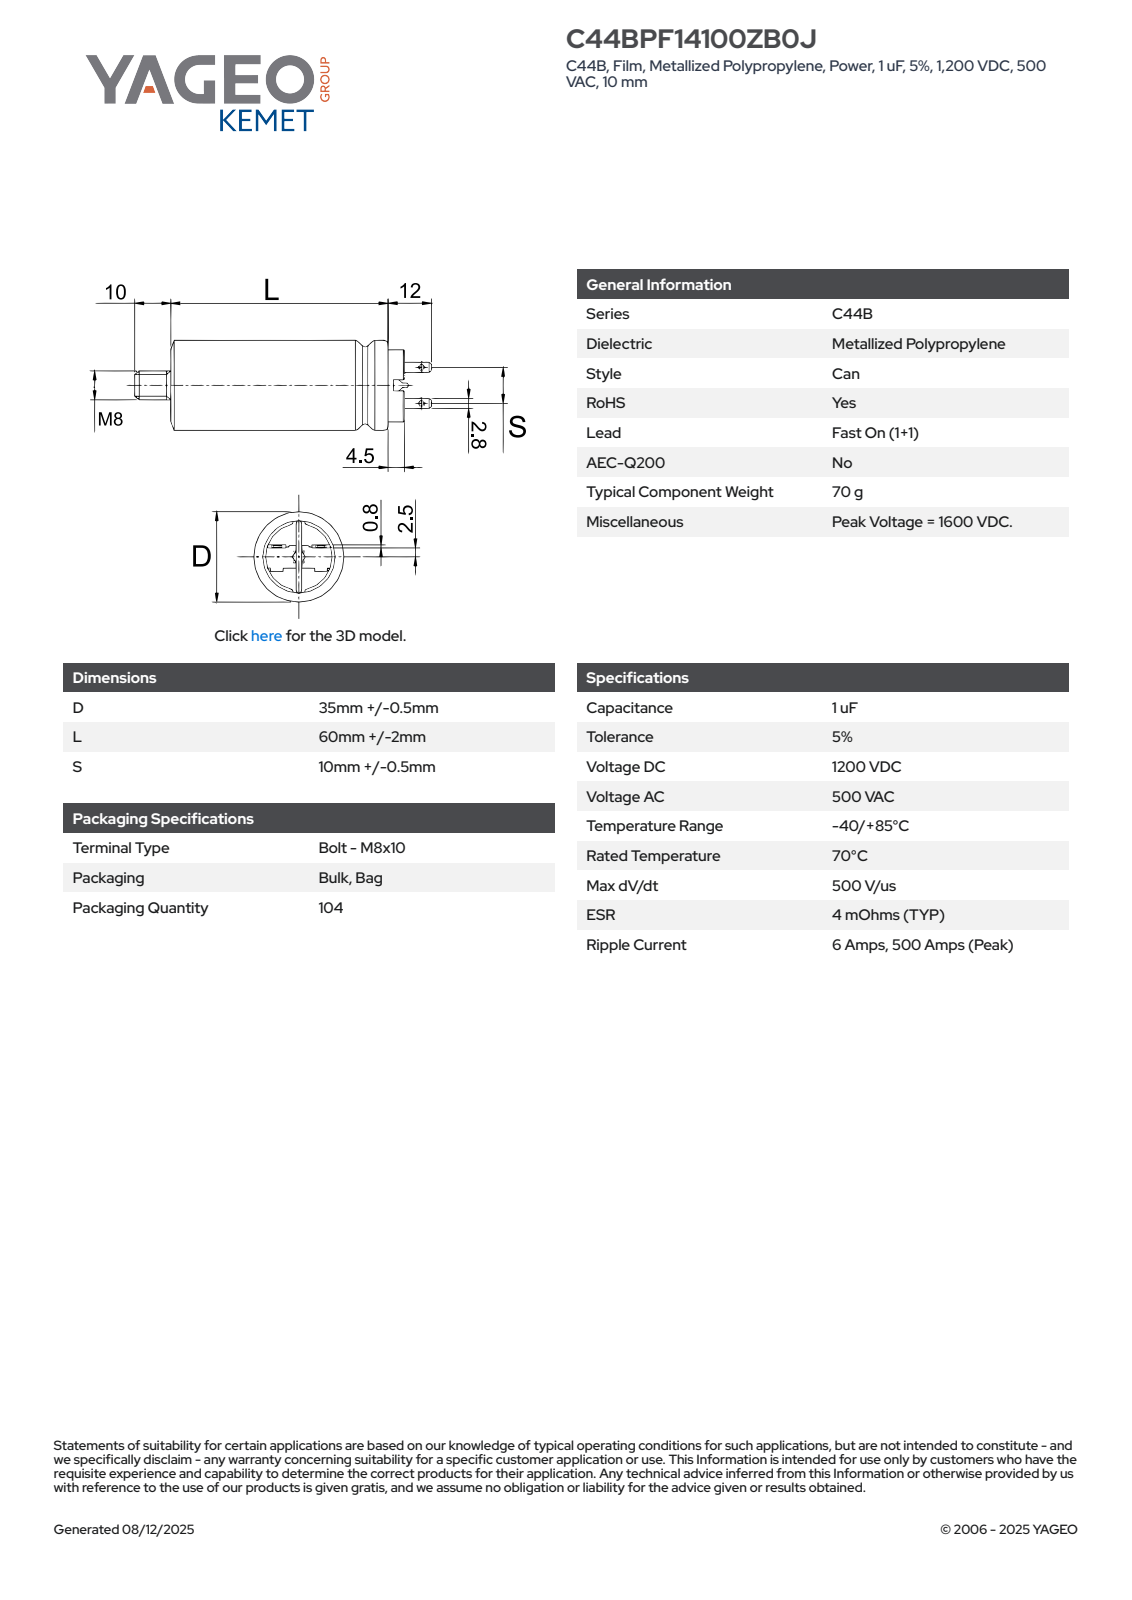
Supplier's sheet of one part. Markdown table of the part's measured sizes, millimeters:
| quantity | value |
| --- | --- |
| part name | CFP_C44B_35X60_D35.5L62S10.5 |
| STEP written by | SolidWorks 2014 (AUTOMOTIVE_DESIGN) |
| units | millimeters |
| bodies | 1 solid, 132 faces (49 planar, 40 cylindrical, 43 other) |
| overall size | 84 × 35.5 × 35.5 |
| volume | 61 830 mm³ |
| surface area | 10 282 mm² |
| round bosses / shafts (diameter × count) | 35.5 × 1, 28.09 × 1, 26.09 × 1, 8 × 1 |
| partial cylindrical surfaces (radius × count) | 0.2 × 6, 0.68 × 1, 17.74 × 1 |
| main face-to-face distances | 62, 66.5, 4.5, 0.8, 10, 72, 76.5, 2.8, 10.5, 2.25 |
